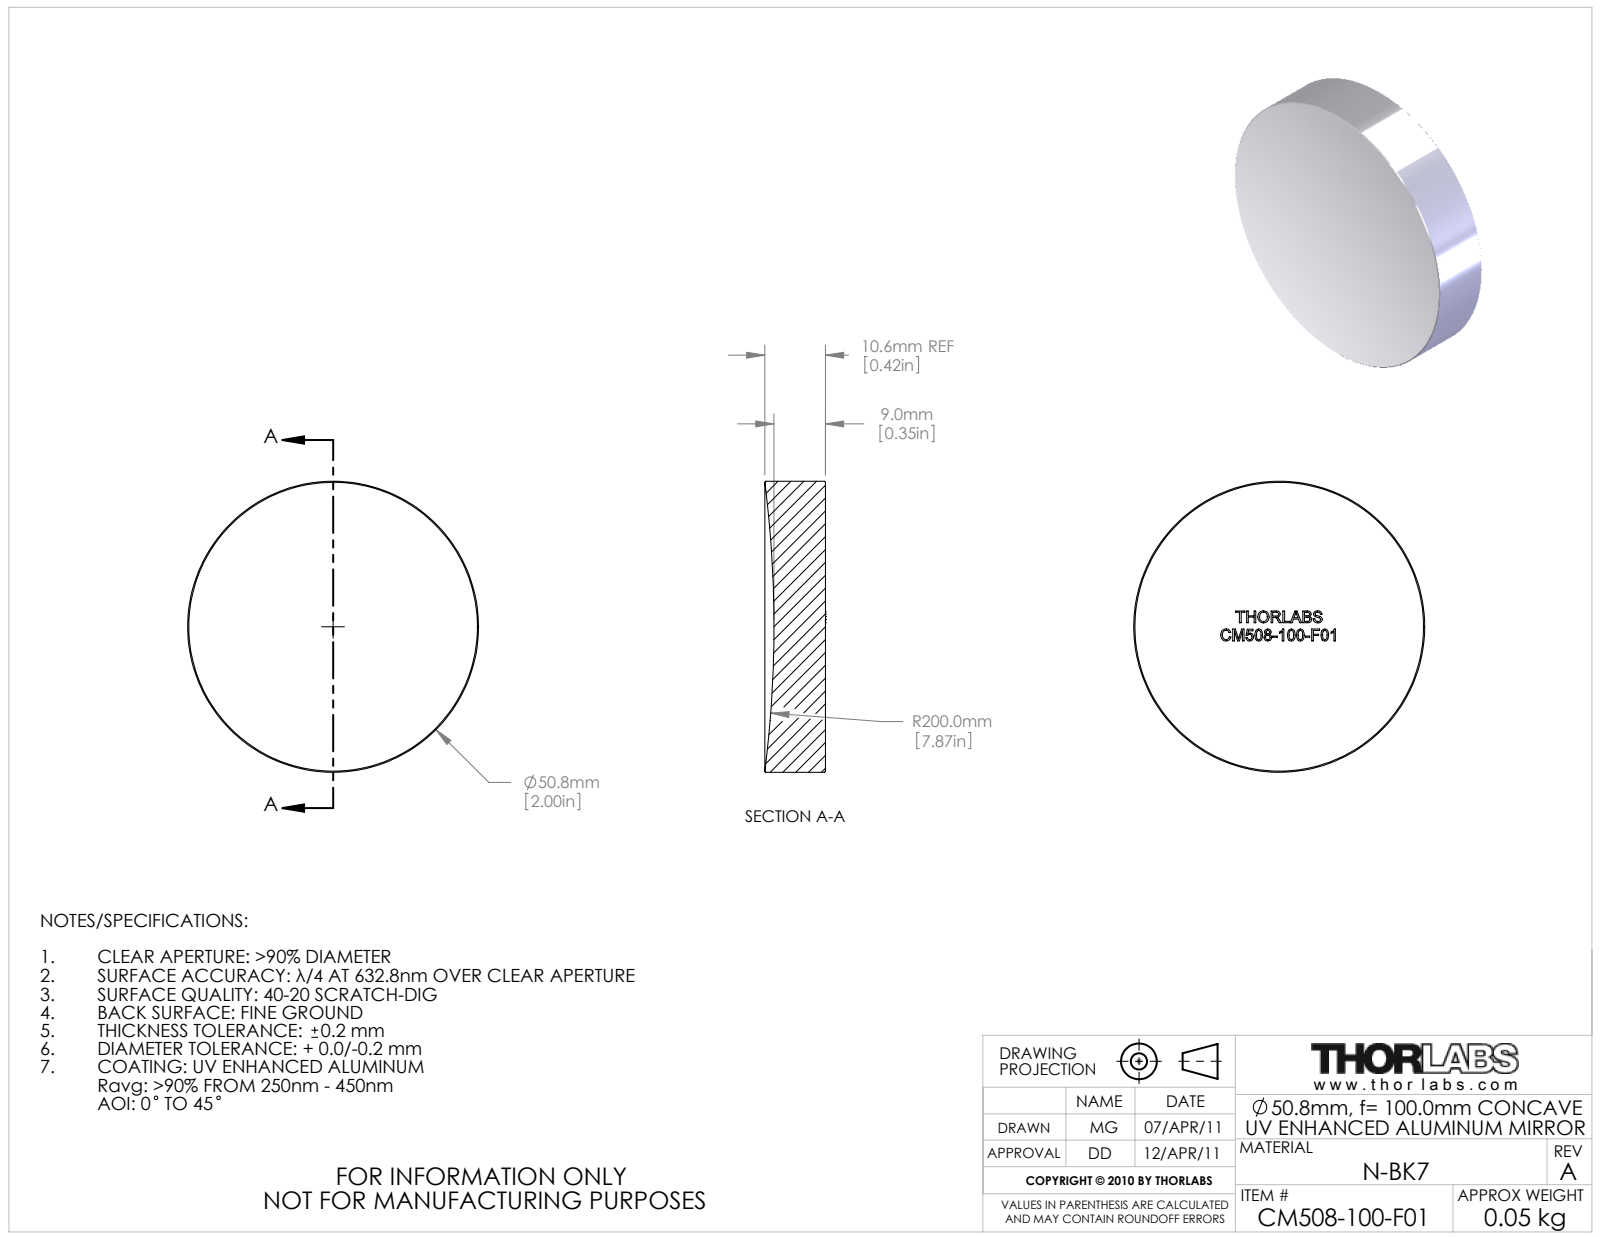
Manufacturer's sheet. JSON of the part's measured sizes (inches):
{"part_name": "22199-E0W", "step_written_by": "SolidWorks 2011 (AUTOMOTIVE_DESIGN)", "units": "inches", "bodies": {"solids": 1, "faces": 271, "planar": 142, "cylindrical": 2, "other": 127}, "overall_size": [2, 2, 0.417], "volume_in3": 1.213, "surface_area_in2": 8.86, "round_bosses_or_shafts": [[2, 1]], "face_to_face_distances": [0.124, 0.081, 0.046, 0.218, 0.344, 0.1, 0.062, 0.029, 0.081, 0.021]}
